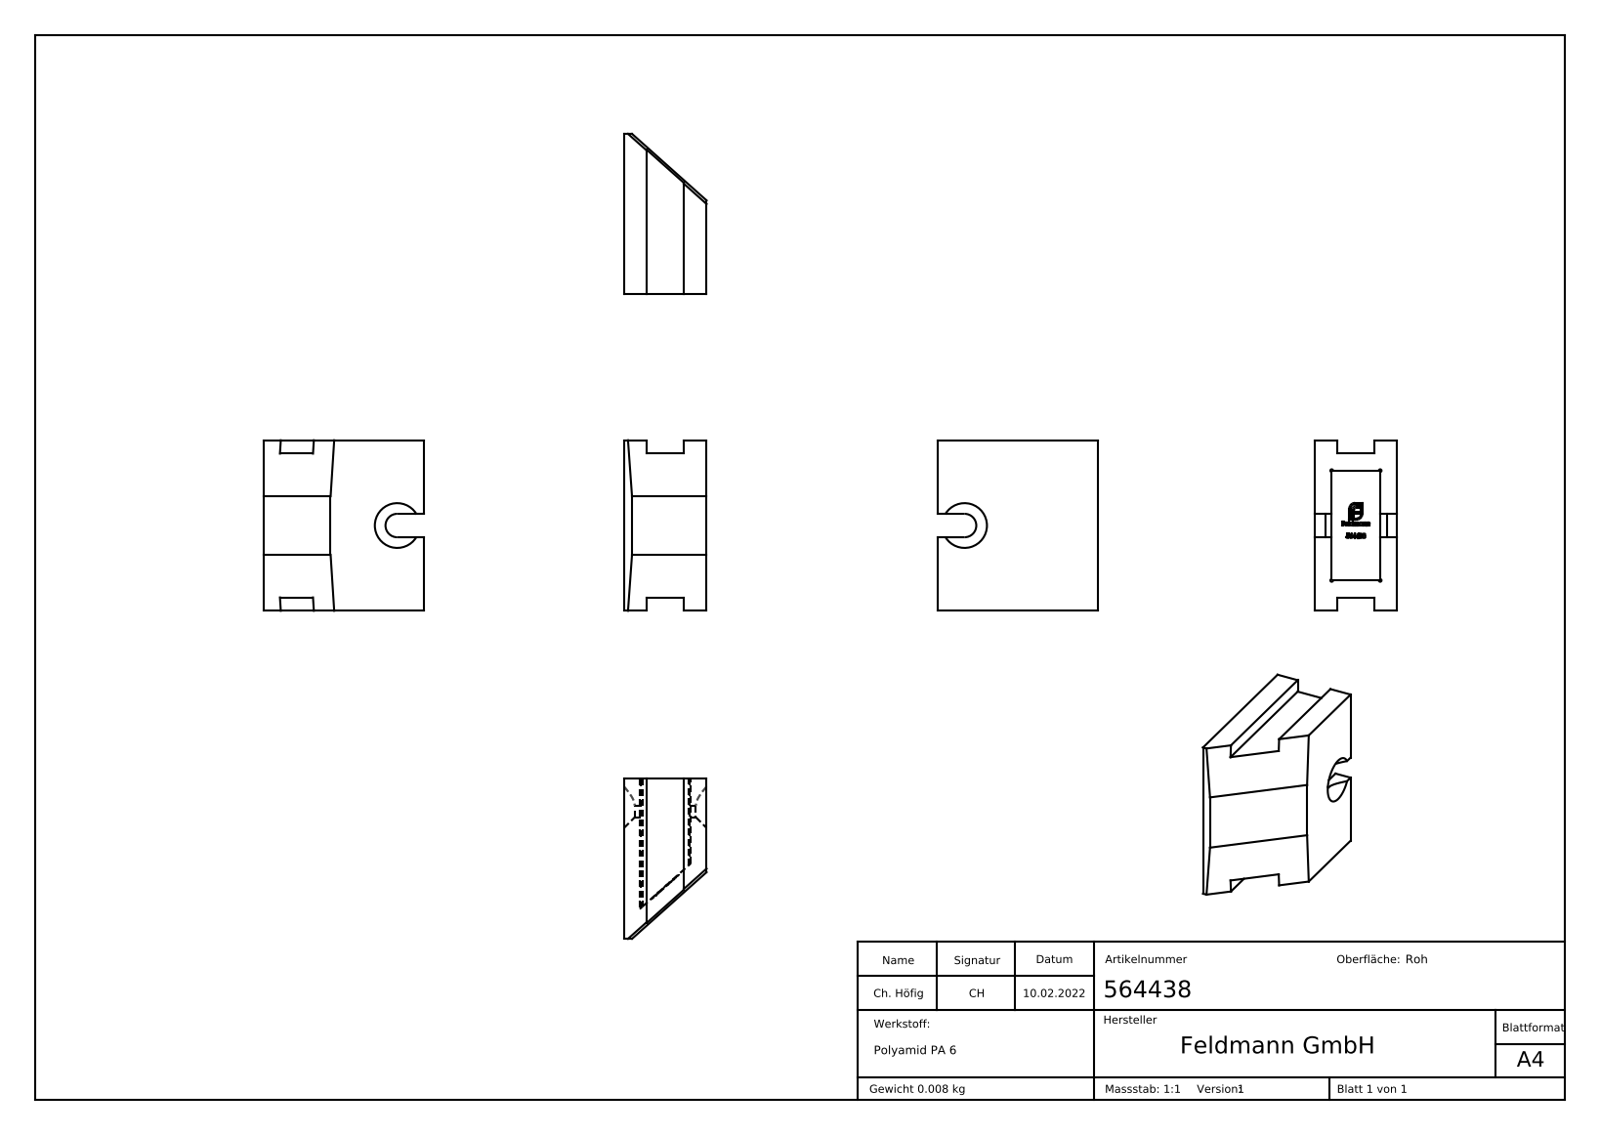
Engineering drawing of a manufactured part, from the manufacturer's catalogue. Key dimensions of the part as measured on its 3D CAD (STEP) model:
Part name (STEP PRODUCT): 564438
STEP written by: SolidWorks 2018 (CONFIG_CONTROL_DESIGN)
Units: millimetres
Bodies: 1 solid, 293 faces (164 planar, 10 cylindrical, 119 other)
Overall size (bounding box): 32 × 30 × 15.5
Volume: 7 125 mm³ · Surface area: 4 821 mm²
Partial cylindrical surfaces — rounded edges, fillets, slot ends (radius × count): R0.25 ×4, R2.2 ×1
Main face-to-face distances: 3.2, 12.3, 15.5, 5.7, 26.3, 2.5, 29.5, 23.8, 9.1, 32
